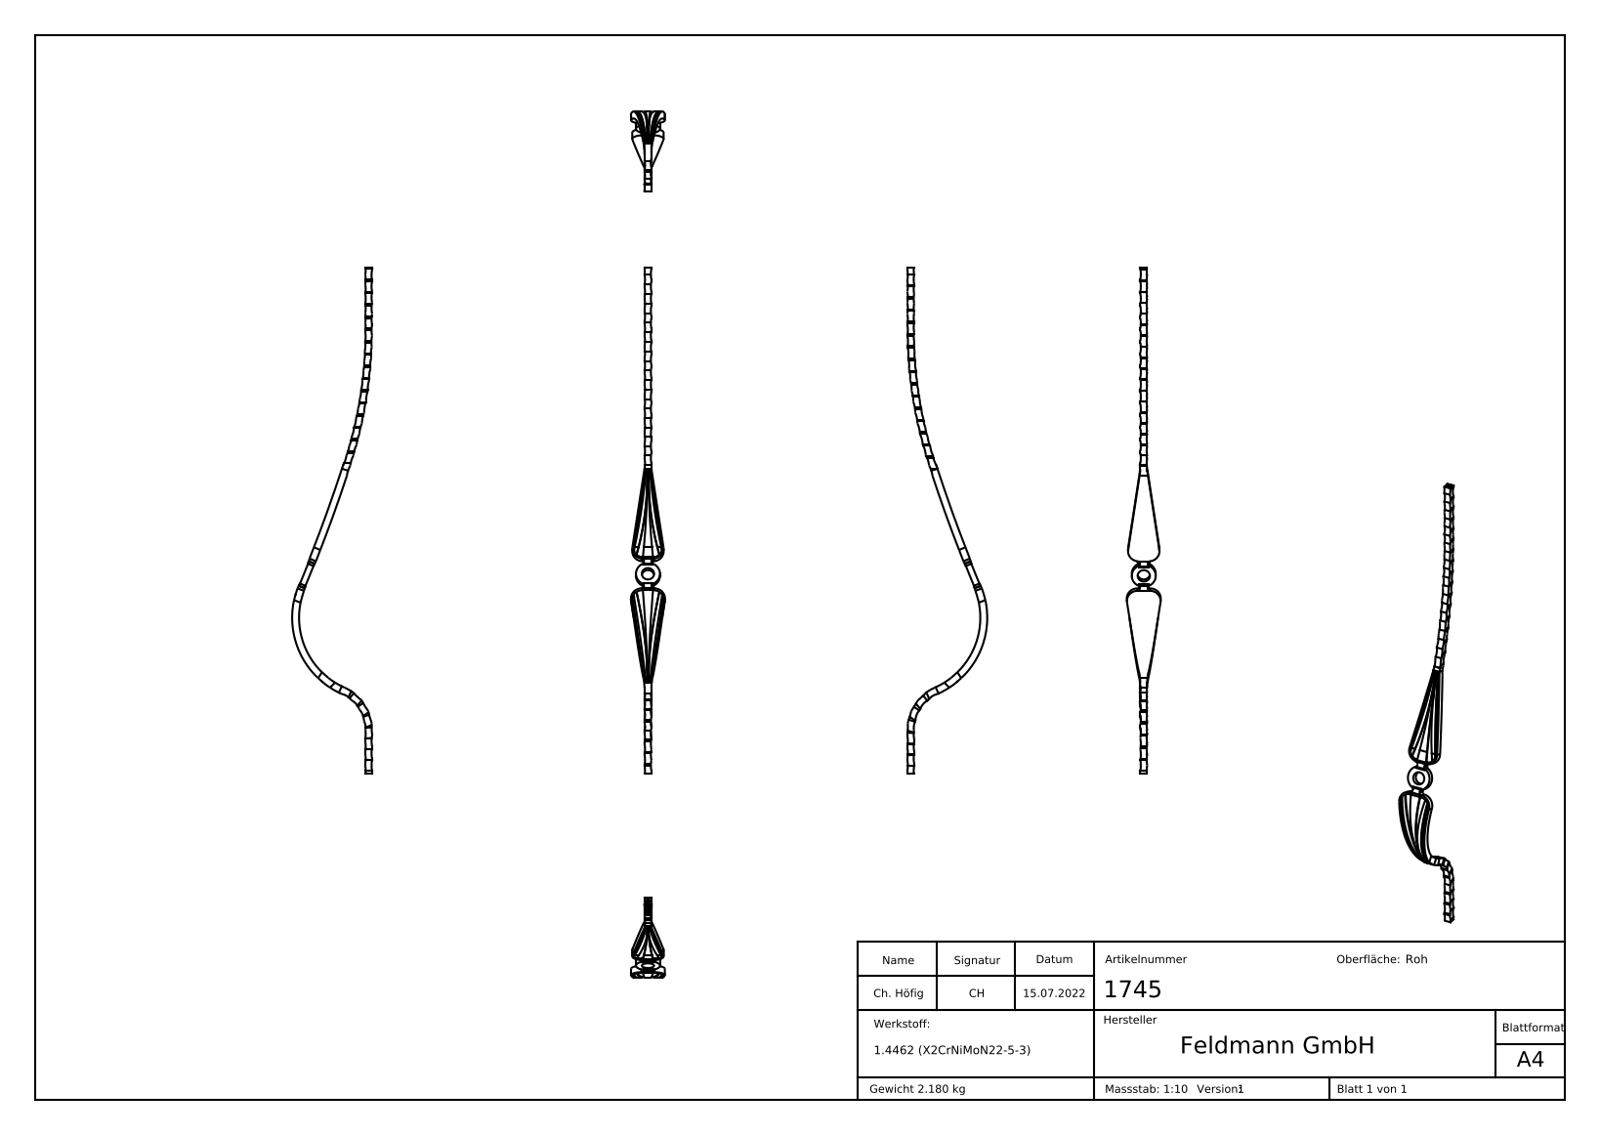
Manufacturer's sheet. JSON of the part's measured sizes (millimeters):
{"part_name": "1745", "step_written_by": "SolidWorks 2018 (CONFIG_CONTROL_DESIGN)", "units": "millimeters", "bodies": {"solids": 1, "faces": 507, "planar": 217, "cylindrical": 155, "other": 135}, "overall_size": [950, 150, 63.8], "volume_mm3": 279515, "surface_area_mm2": 77791, "round_holes": [[23, 1]], "partial_cylinders_radius": [[50.5, 95], [5, 4], [20, 4], [30.43, 4], [120.12, 4], [7.99, 2], [9.56, 2], [118, 2]], "face_to_face_distances": [13, 950, 1, 14, 15, 949.9, 177.1, 173.46, 7.75, 0.57]}
